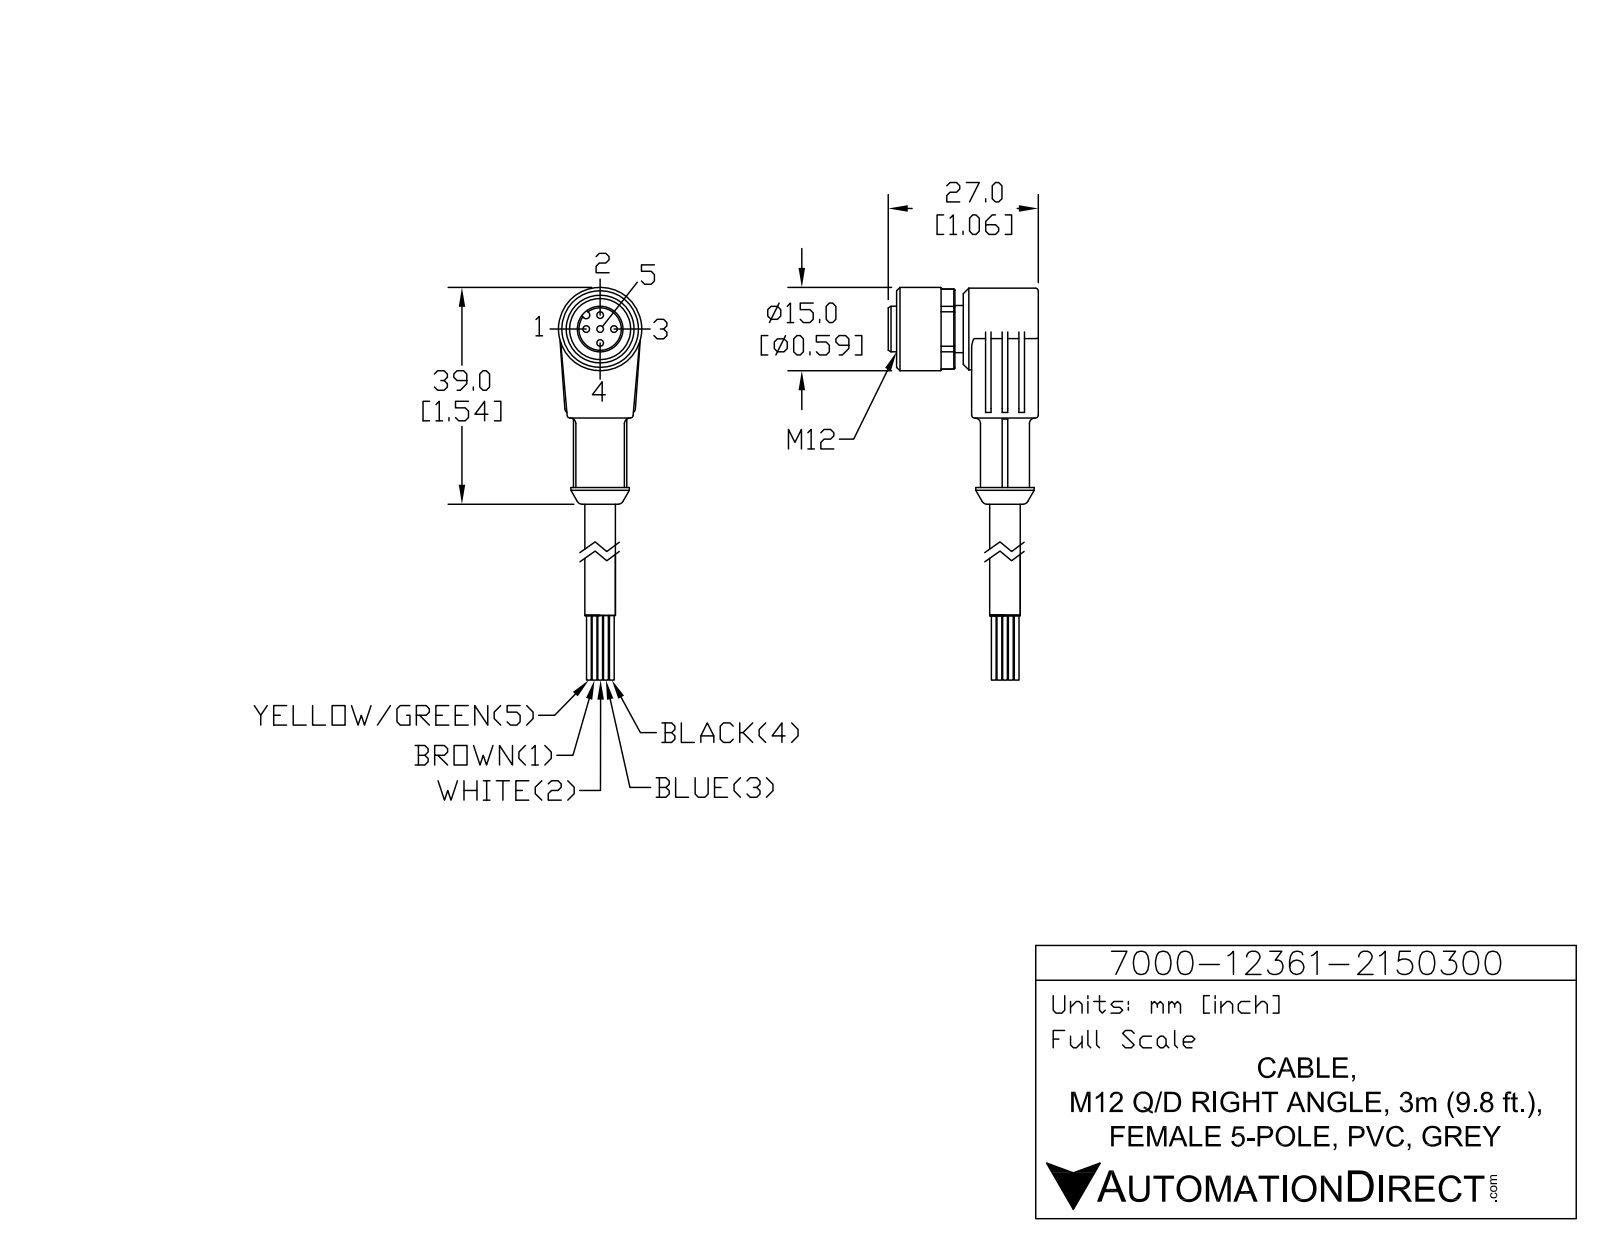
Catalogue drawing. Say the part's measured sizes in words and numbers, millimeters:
The part is named "7000-12361-2150300". Its 3-D file was written by "SolidWorks 2015 (AUTOMOTIVE_DESIGN)". It is 1 solid with 150 faces: 61 planar, 60 cylindrical and 29 other. Overall it measures 59 by 27 by 15 millimeters. Its volume is 6 805 cubic millimeters and its surface area 3 613 square millimeters. Round holes: 5 of diameter 1.2, 1 of diameter 4.8, 1 of diameter 11. Round bosses or shafts: 1 of diameter 15, 1 of diameter 14.7, 1 of diameter 10.5, 1 of diameter 8.8, 1 of diameter 8.5, 1 of diameter 8.2, 1 of diameter 5.5. Partial cylindrical surfaces (rounded edges, fillets, slot ends): 8 of radius 0.5, 2 of radius 1, 1 of radius 0.65, 1 of radius 7.2. The main face-to-face distances are 12, 1.5, 3, 13.5, 15, 5.5, 9.5, 6, 8, 12.5. The hole center spacings are 2.5, 3.54, 5.
